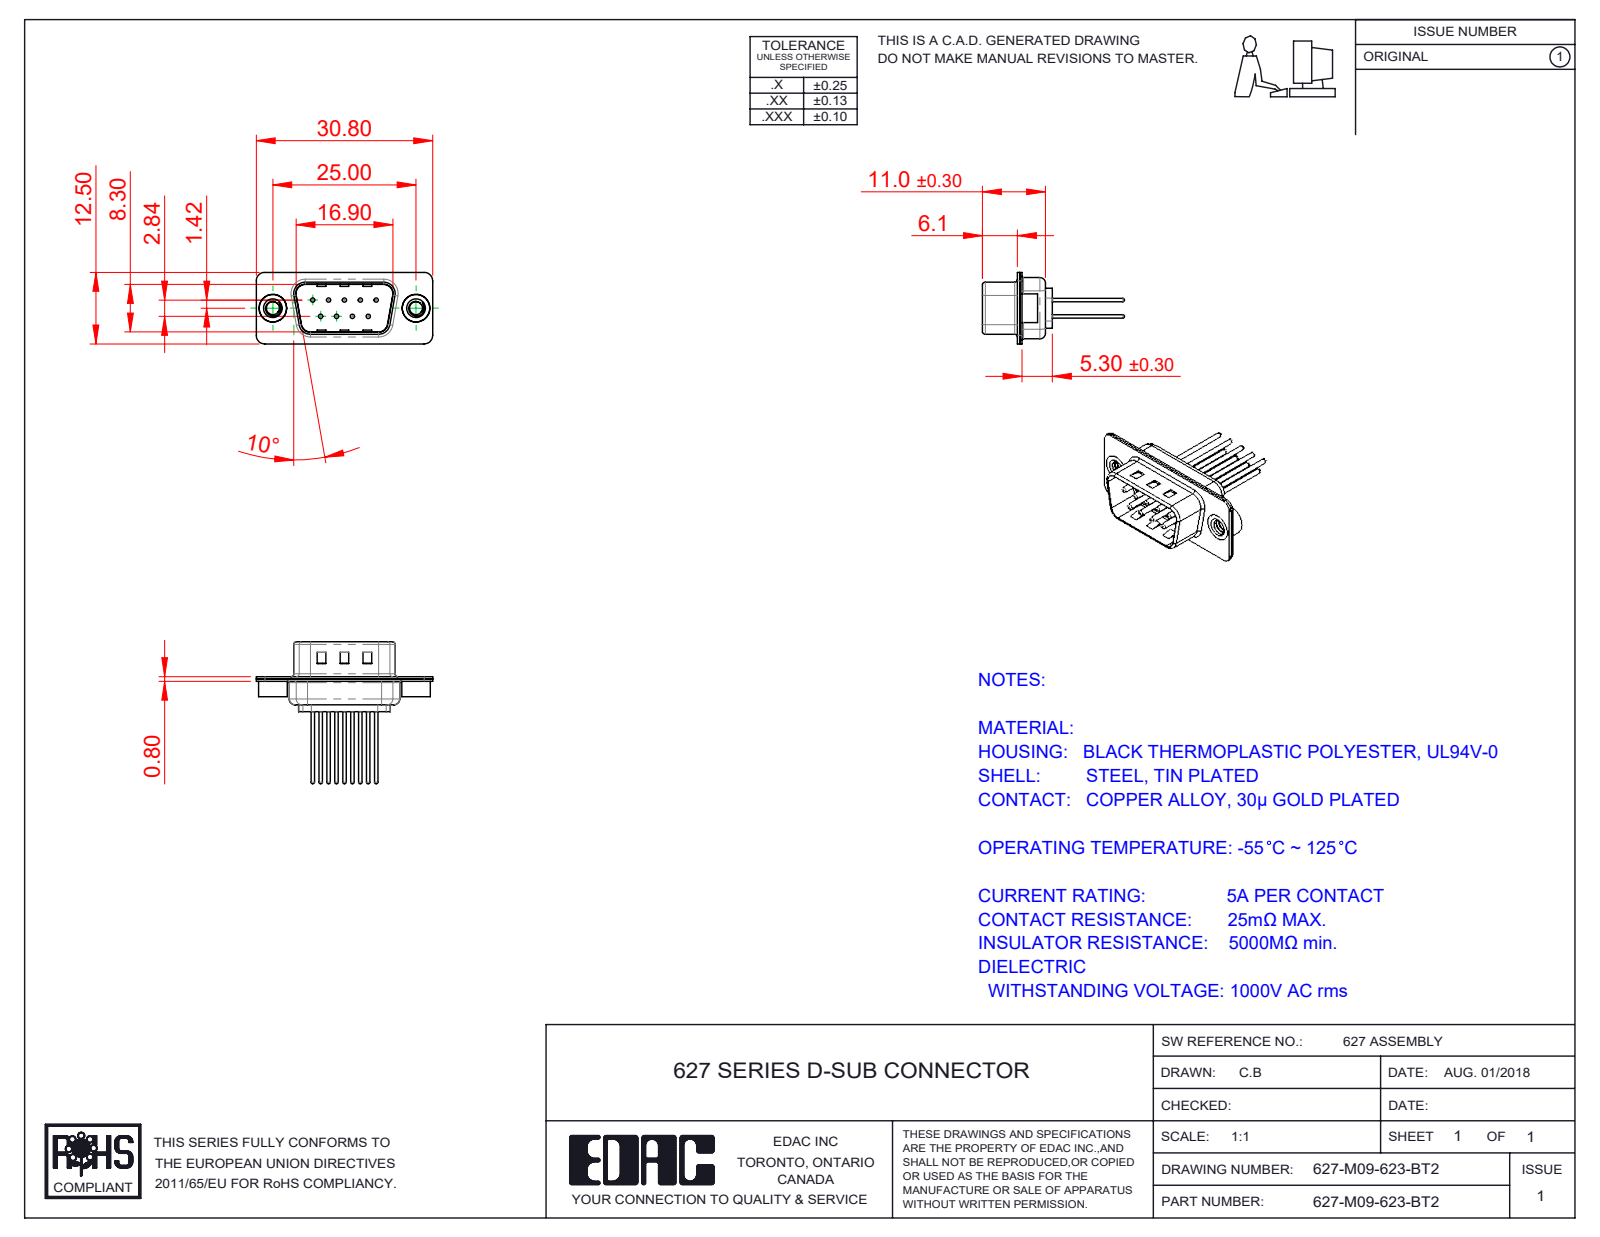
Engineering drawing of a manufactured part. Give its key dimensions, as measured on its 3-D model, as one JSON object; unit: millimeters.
{"part_name": "627M 4-40 Threaded Rivet; 627M Contact Row 1_23; 627M Shell Front_09 Contacts; 627-M09-623-BT2 (+3 more)", "step_written_by": "SolidWorks 2020 (CONFIG_CONTROL_DESIGN)", "units": "millimeters", "bodies": {"solids": 14, "faces": 637, "planar": 170, "cylindrical": 255, "other": 212}, "overall_size": [30.8, 24.77, 12.5], "volume_mm3": 1328, "surface_area_mm2": 3691, "round_holes": [[0.75, 9], [1.6, 9], [2, 9], [2.26, 2], [4, 2], [4.8, 2]], "round_bosses_or_shafts": [[1.5, 9], [0.6, 9], [5, 2], [4.9, 2]], "partial_cylinders_radius": [[1.5, 16], [2, 12], [0.5, 8], [1.6, 8], [0.25, 4], [0.6, 4], [0.65, 4], [0.9, 4]], "face_to_face_distances": [0.4, 0.8, 9.5, 9.1, 8.7, 0.65, 9.9, 1.2, 6.1, 5.3], "hole_center_spacings": [3.16, 2.77, 5.54, 5.03, 5.04, 8.31, 7.1, 7.48]}
